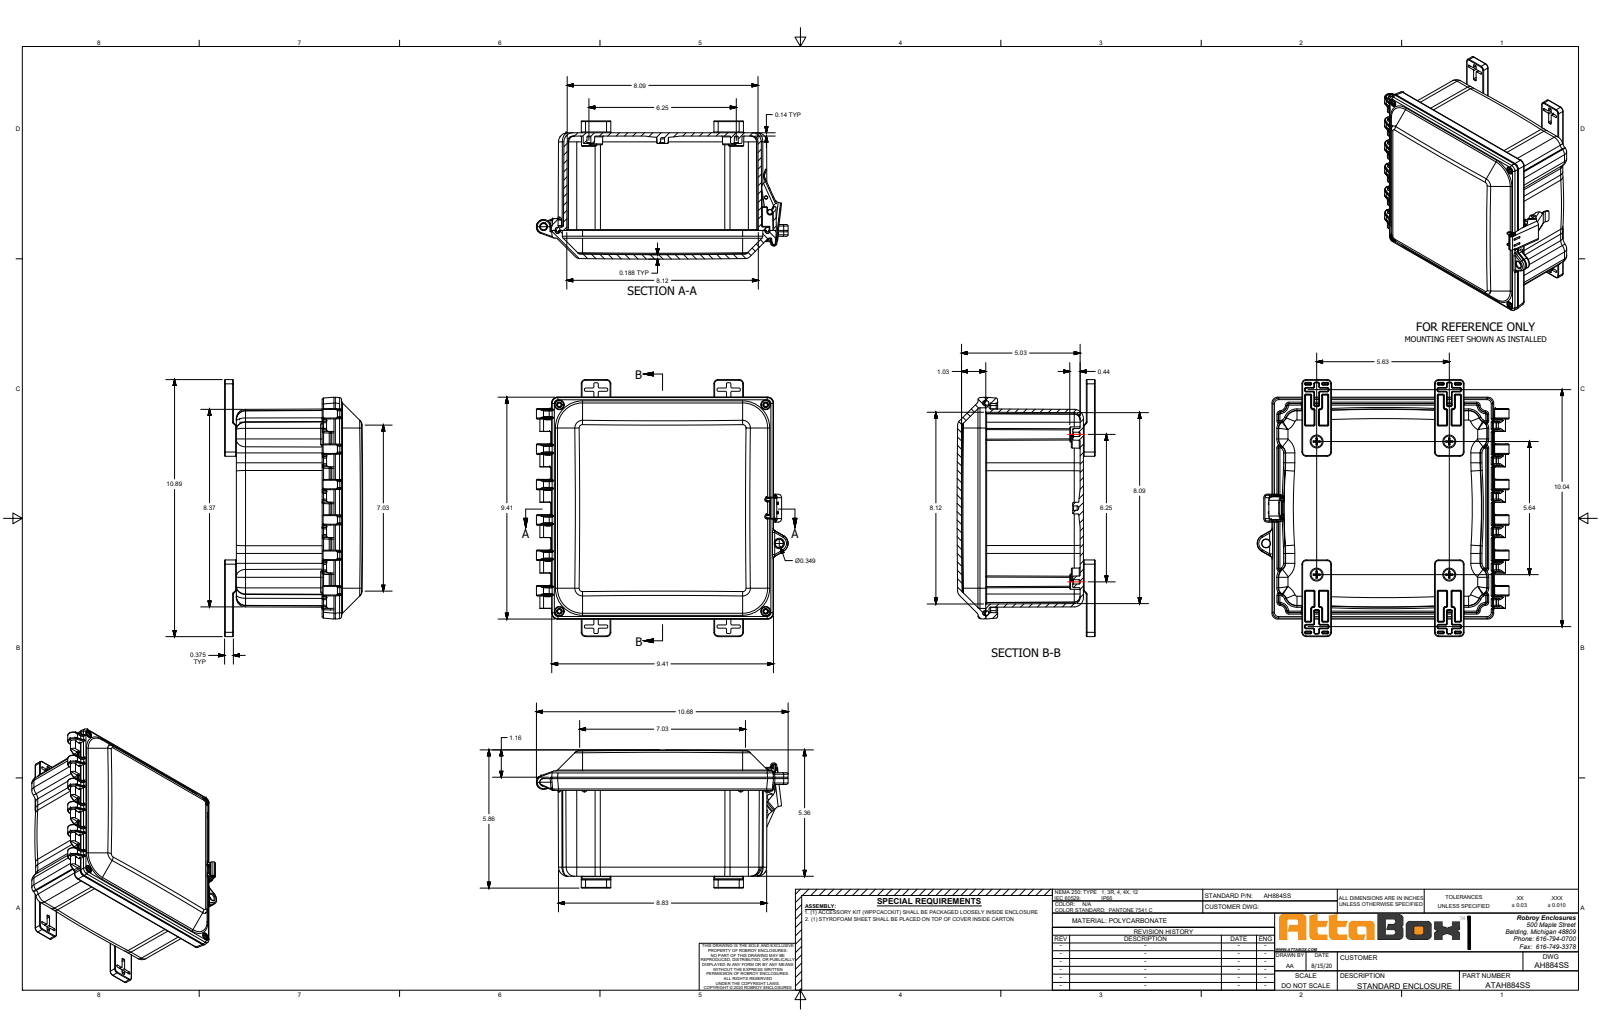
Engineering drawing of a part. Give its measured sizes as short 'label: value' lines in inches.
name: AH884
written by: SolidWorks 2019 (AUTOMOTIVE_DESIGN)
unit: in
bodies: 25 solids, 4007 faces (937 planar, 1462 cylindrical, 1608 other)
size: 10.892 × 10.676 × 5.858
volume: 66.85 in³; area: 842.7 in²
holes: 8× ⌀0.156, 8× ⌀0.26, 4× ⌀0.195, 4× ⌀0.196, 4× ⌀0.25, 4× ⌀0.265, 4× ⌀0.313, 4× ⌀0.323, 4× ⌀0.39, 1× ⌀0.327, 1× ⌀0.375, 1× ⌀0.45
bosses: 8× ⌀0.315, 4× ⌀0.394, 4× ⌀0.25, 2× ⌀0.2, 1× ⌀0.313
rounds: 160× R0.03, 154× R0.035, 128× R0.065, 126× R0.015, 104× R0.02, 84× R0.05, 27× R0.01, 25× R0.025
face distances: 0.14, 4.14, 4, 0.191, 0.5, 0.64, 4.64, 0.14, 0.265, 0.375
hole spacings: 7.604, 5.633, 8.397, 1.768, 2.209, 5.625, 5.946, 5.946
